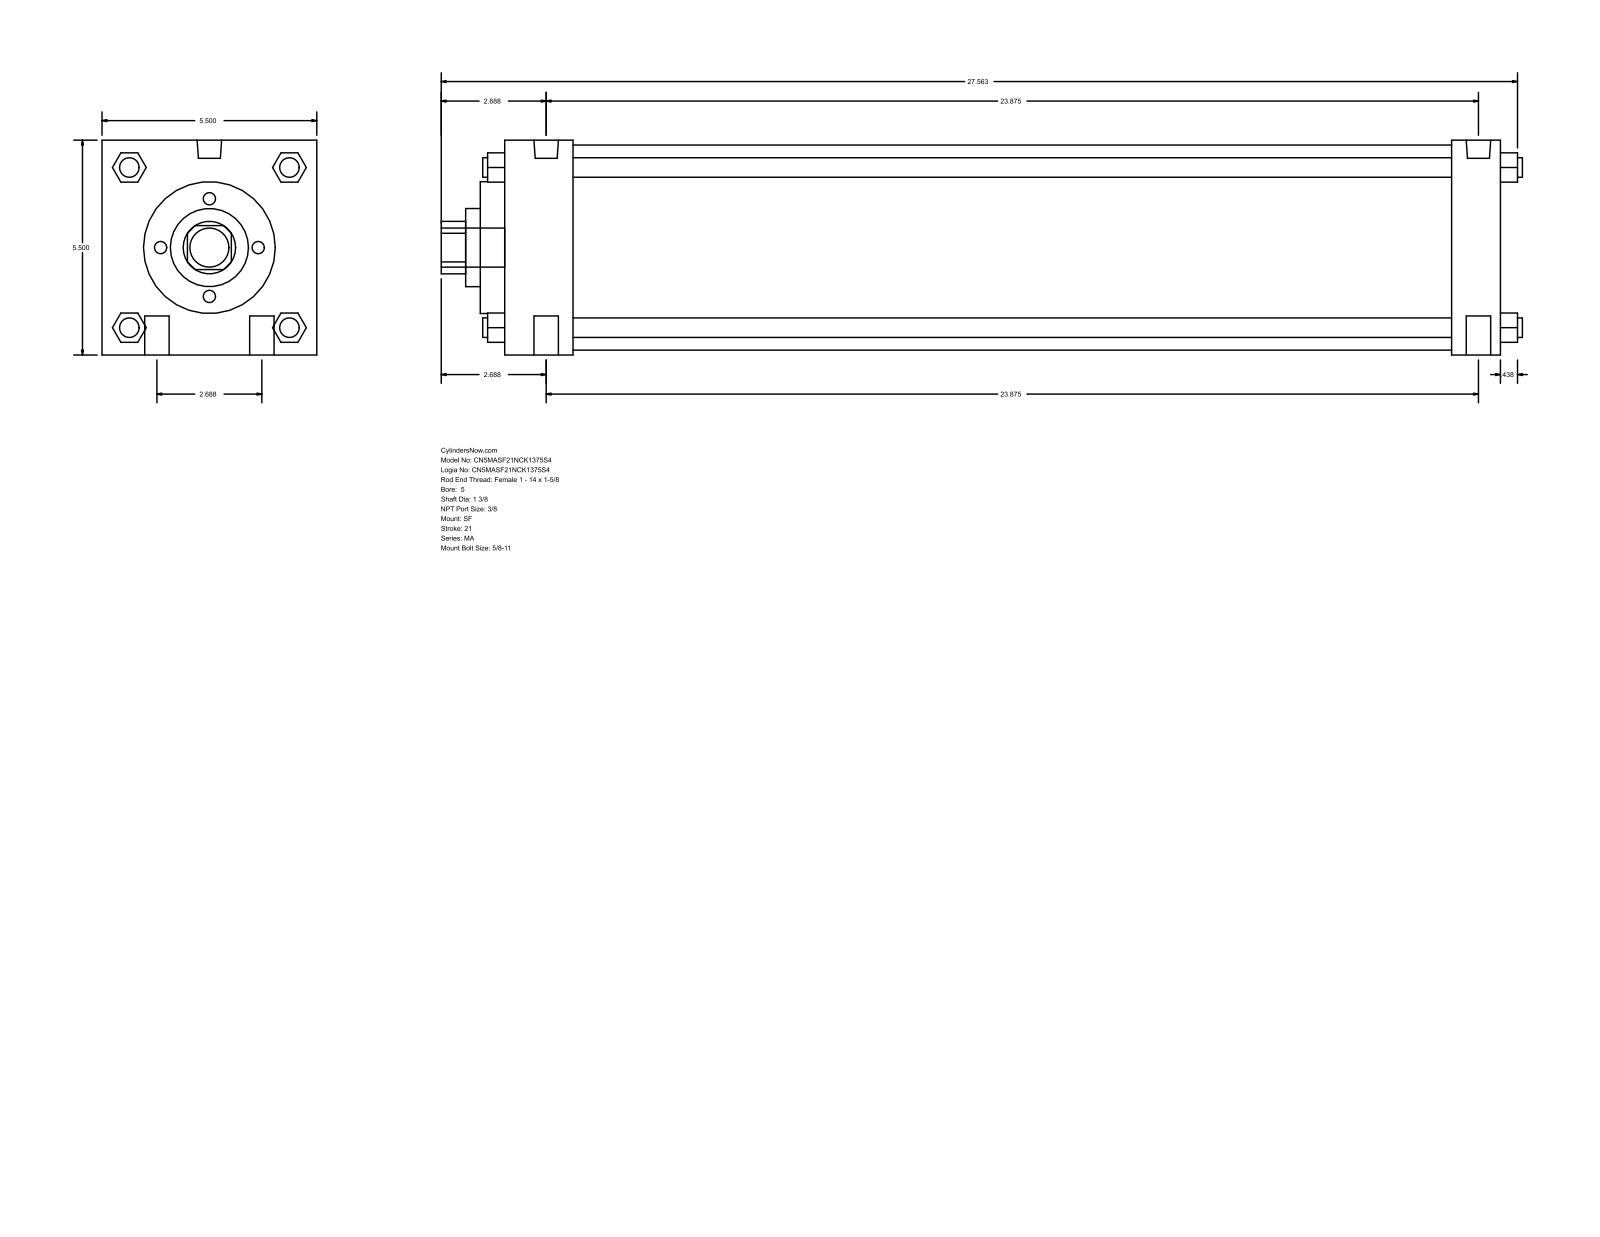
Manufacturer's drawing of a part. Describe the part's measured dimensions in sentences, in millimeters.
The part is named "MA_SF__0500_1.375". Its 3-D file was written by "GSSL Pune (CONFIG_CONTROL_DESIGN)". It is 0 solids with 126 faces: 95 planar, 31 cylindrical and 0 other. Overall it measures 703.26 by 139.7 by 139.7 millimeters. Round holes: 1 of diameter 34.92, 1 of diameter 50.8, 1 of diameter 85.72, 1 of diameter 133.35. Round bosses or shafts: 4 of diameter 15.88, 4 of diameter 12.7, 2 of diameter 15.93, 2 of diameter 11.11, 1 of diameter 25.4. Partial cylindrical surfaces (rounded edges, fillets, slot ends): 1 of radius 17.06. The main face-to-face distances are 139.7, 647.71, 44.45, 615.96, 571.51, 603.26, 31.75, 15.87, 60.32, 631.83.
